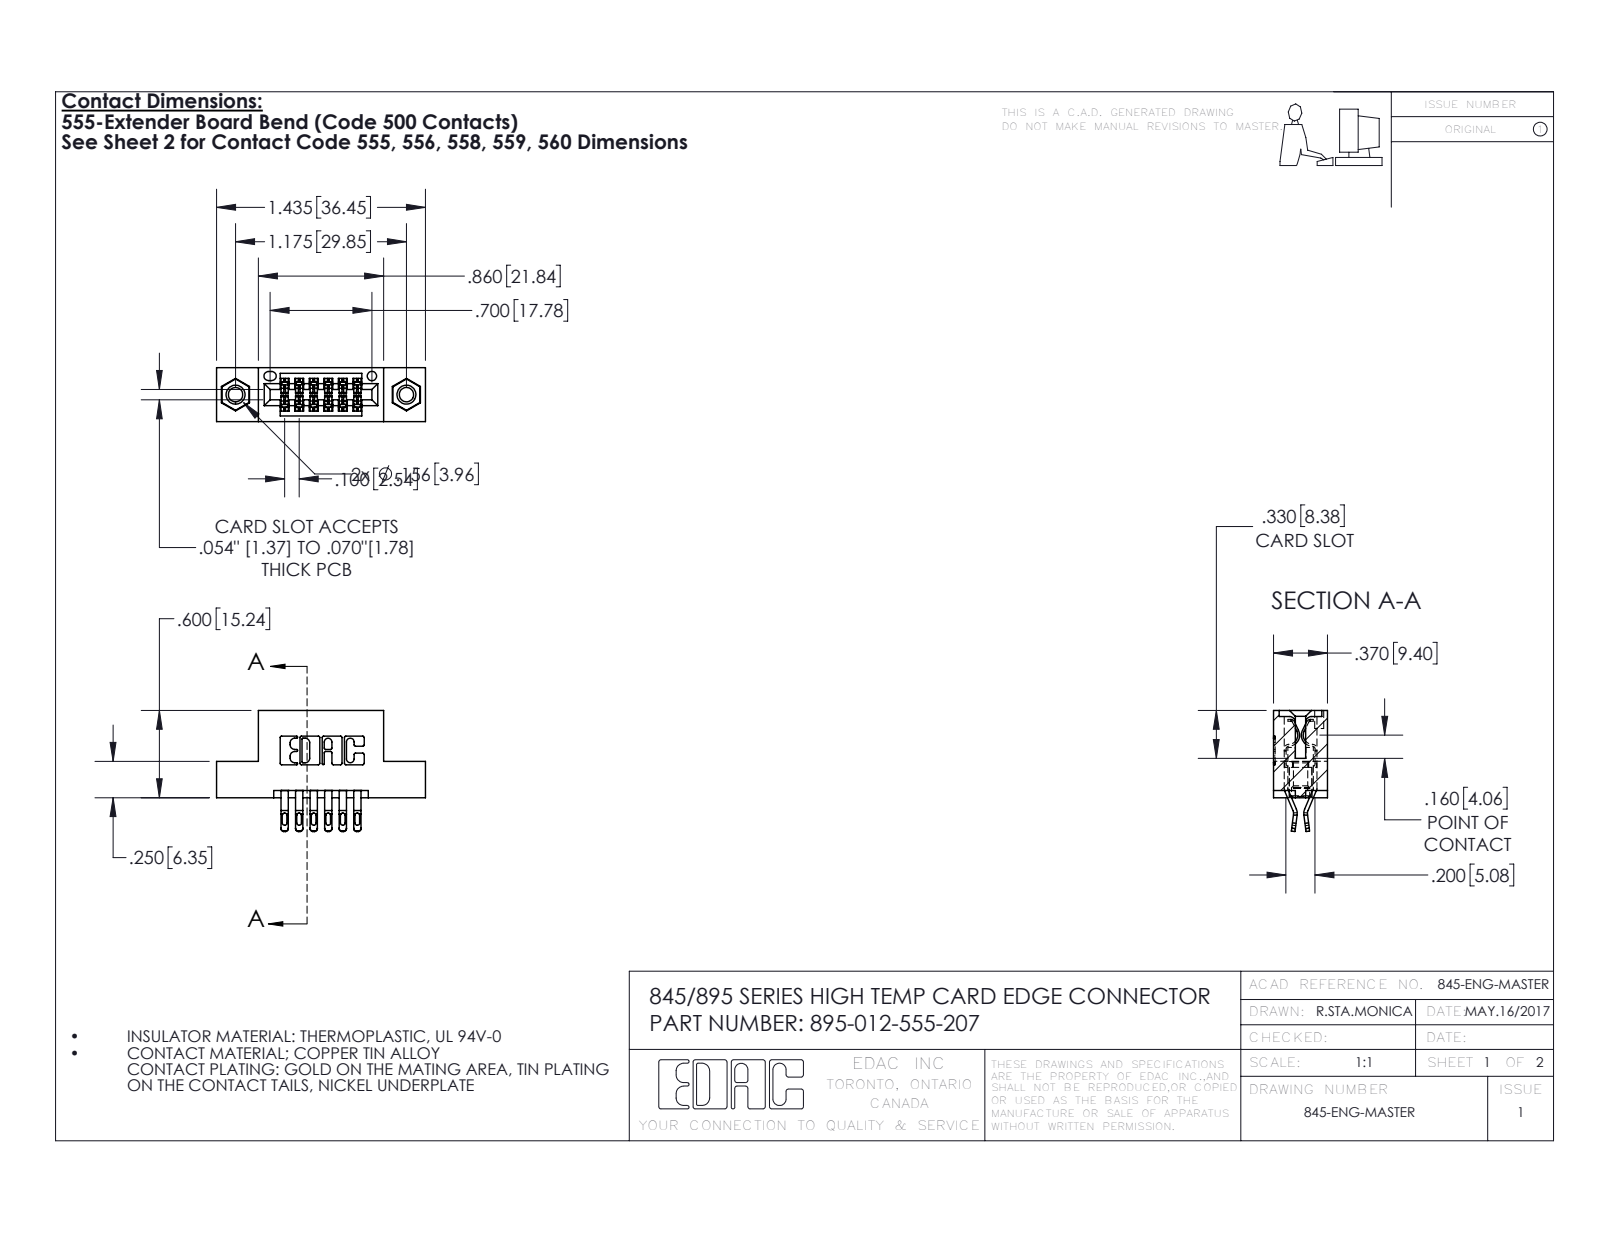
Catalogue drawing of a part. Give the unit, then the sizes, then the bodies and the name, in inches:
Units: inches
Overall size (bounding box): 1.435 × 0.832 × 0.37
Round holes (diameter × count): ⌀0.098 ×2, ⌀0.125 ×2, ⌀0.156 ×2, ⌀0.064 ×1
Round bosses / shafts (diameter × count): ⌀0.155 ×2
Partial cylindrical surfaces — rounded edges, fillets, slot ends (radius × count): R0.016 ×30, R0.02 ×24, R0.01 ×22, R0.006 ×18, R0.007 ×6, R0.031 ×6, R0.026 ×3, R0.01 ×2
Main face-to-face distances: 0.2, 0.37, 0.072, 0.298, 0.1, 0.025, 0.3, 0.098, 0.272, 0.35
Hole centre spacings: 0.27, 0.946, 1.175
Volume: 0.197 in³ · Surface area: 6.546 in²
Bodies: 15 solids, 858 faces (484 planar, 358 cylindrical, 16 other)
Part name (STEP PRODUCT): 345 Part_Flush Mounting Lugs - 0.156 Dia-TI; 395-012-555-207; 345-292-001_555 Tail; 345-250-001_345-250-005-103
STEP written by: SolidWorks 2016 (CONFIG_CONTROL_DESIGN)
